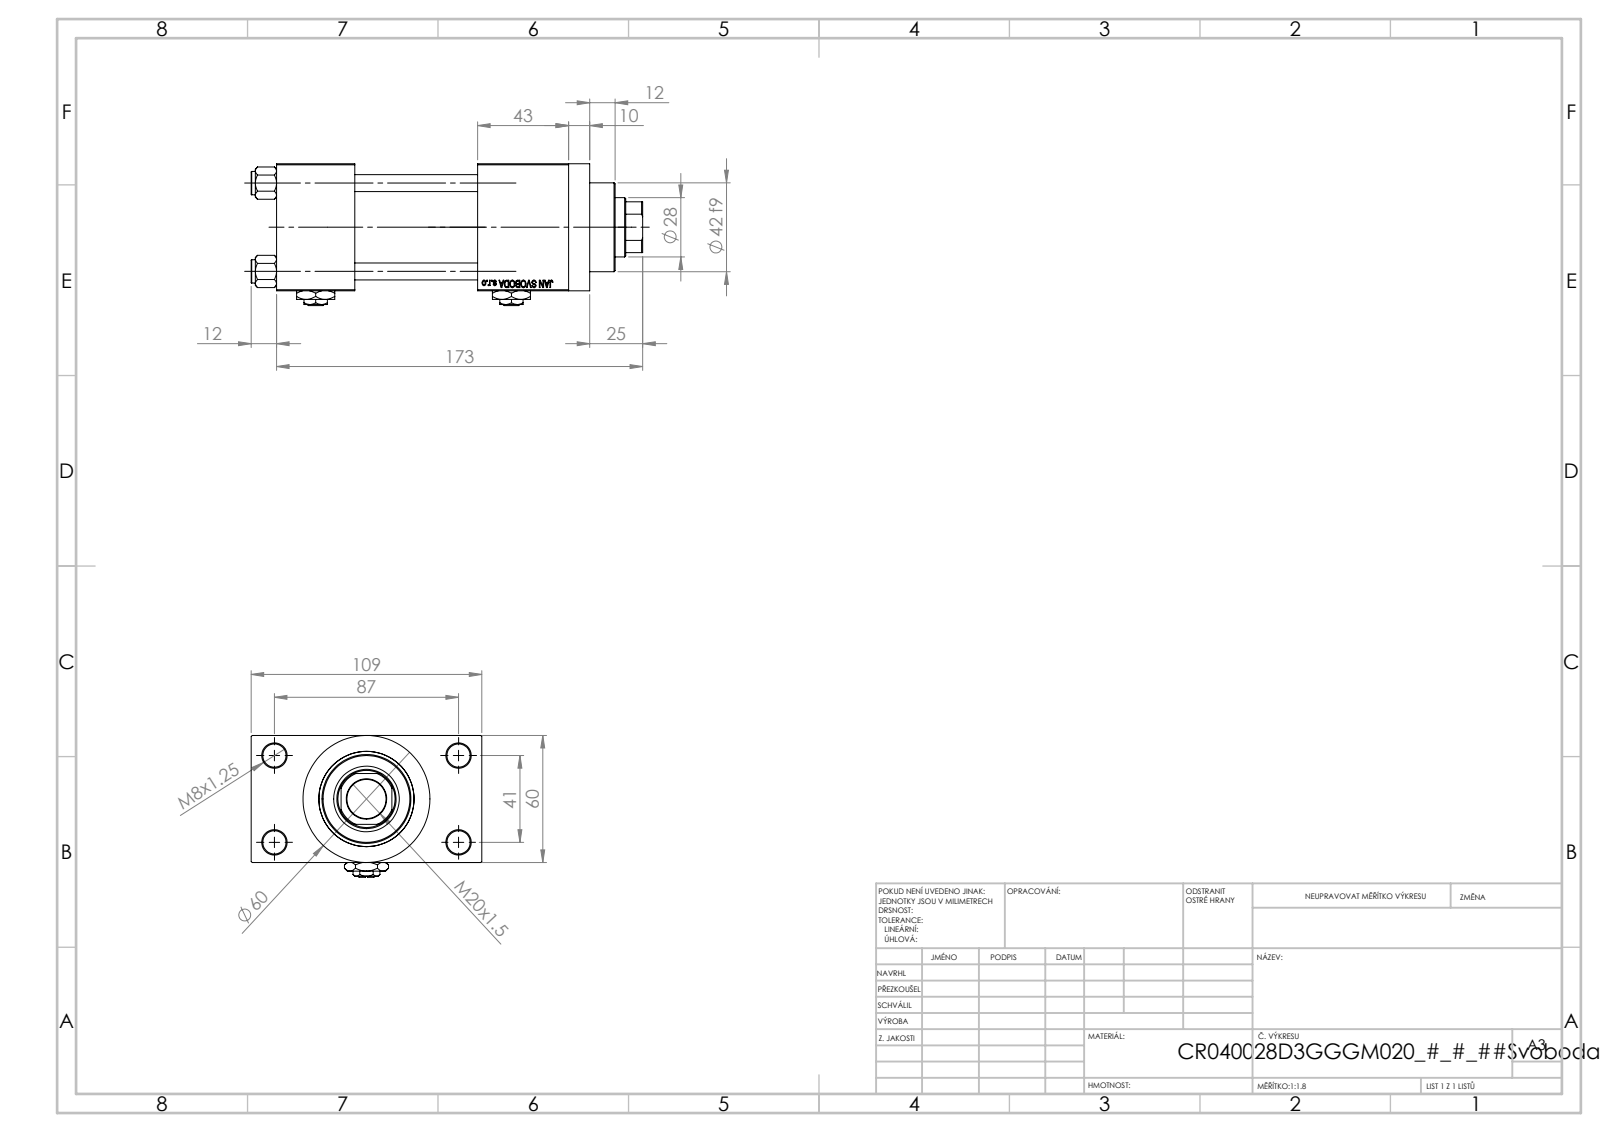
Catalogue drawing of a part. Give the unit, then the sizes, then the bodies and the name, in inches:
Units: inches
Overall size (bounding box): 7.283 × 4.291 × 2.638
Round holes (diameter × count): ⌀0.315 ×4, ⌀0.433 ×4, ⌀0.276 ×2, ⌀0.656 ×2, ⌀0.945 ×2, ⌀0.728 ×1, ⌀1.102 ×1, ⌀1.22 ×1, ⌀1.575 ×1, ⌀1.772 ×1
Round bosses / shafts (diameter × count): ⌀0.433 ×4, ⌀2.362 ×1, ⌀1.811 ×1, ⌀1.654 ×1
Partial cylindrical surfaces — rounded edges, fillets, slot ends (radius × count): R0.531 ×1
Main face-to-face distances: 2.362, 3.327, 0.965, 2.283, 1.457, 3.74, 5.433, 3.976, 1.693, 4.291
Hole centre spacings: 0.892, 1.161, 1.642, 1.856, 1.893, 2.533, 3.011, 1.614
Volume: 32.46 in³ · Surface area: 202.2 in²
Bodies: 13 solids, 1206 faces (546 planar, 100 cylindrical, 560 other)
Part name (STEP PRODUCT): V215CR_VCP_D; NUT_M5_D; V215CR_D_TYCINKA; V215_VC_A (+2 more)
STEP written by: SolidWorks 2019 (CONFIG_CONTROL_DESIGN)
